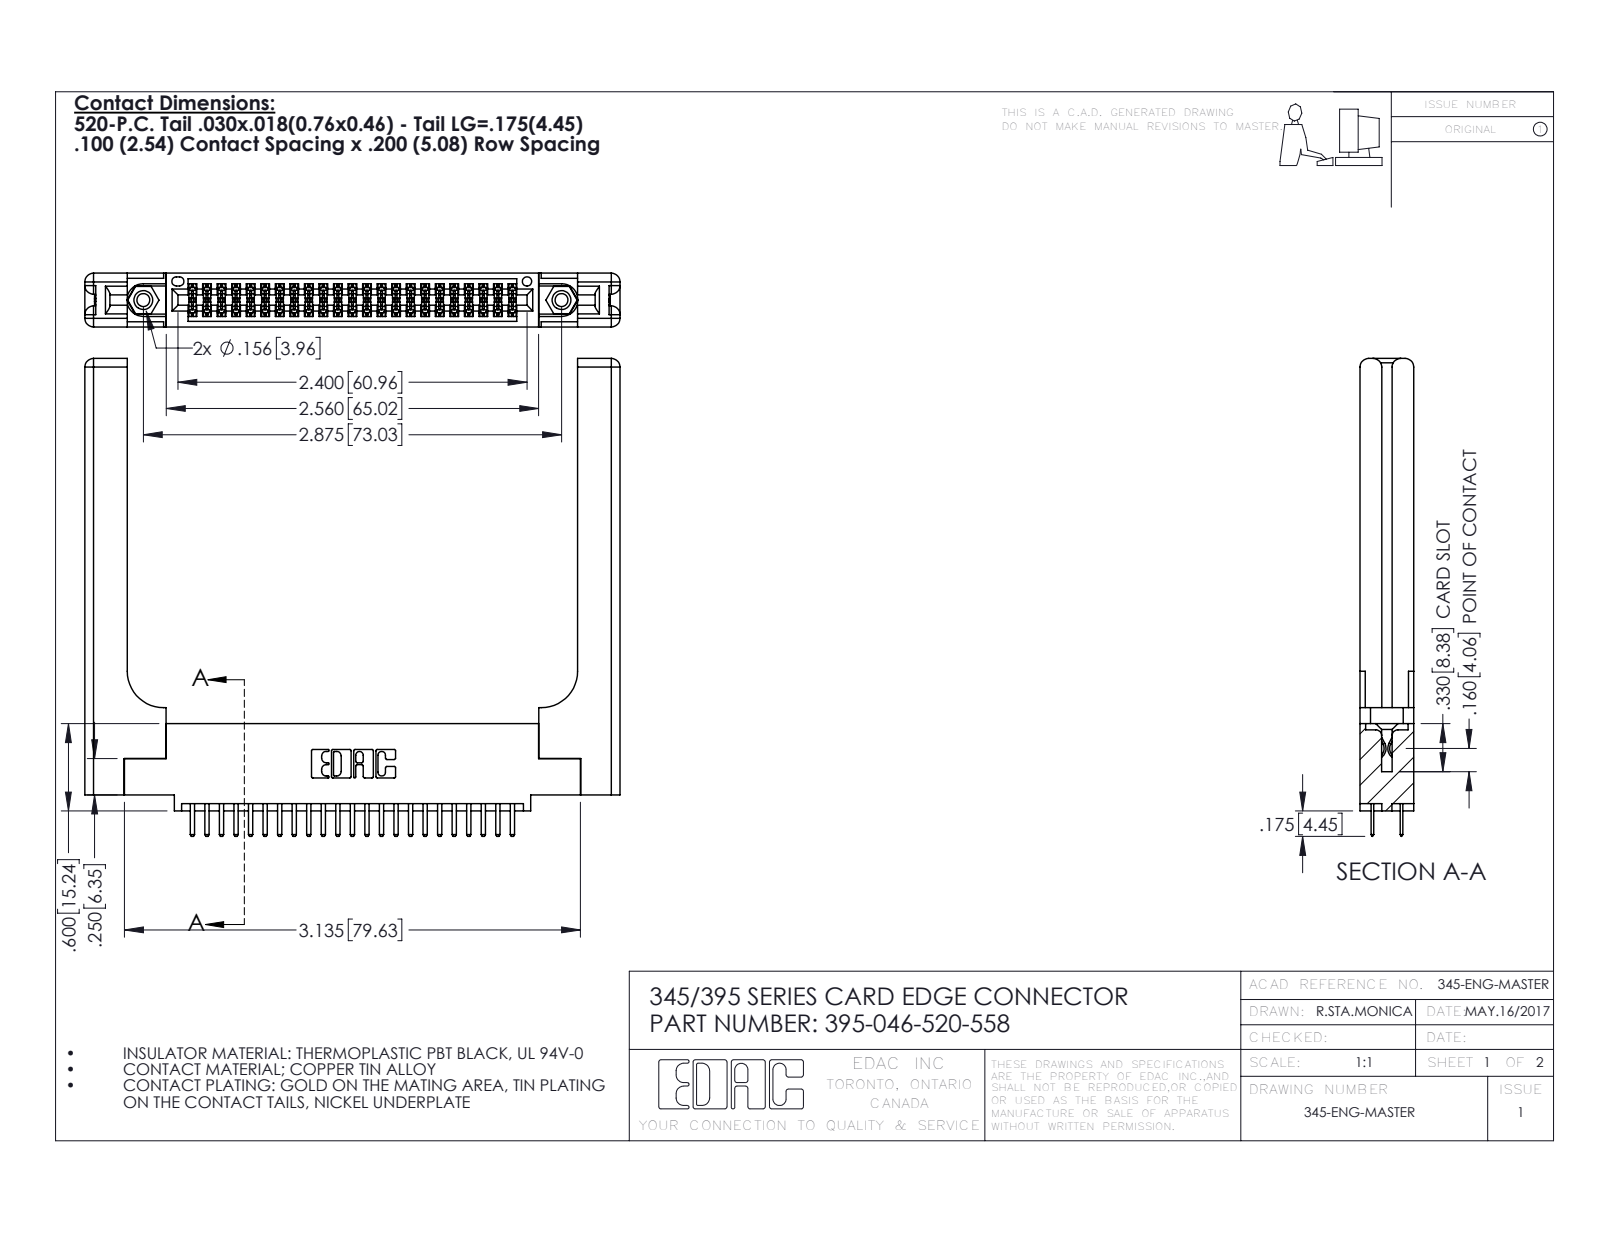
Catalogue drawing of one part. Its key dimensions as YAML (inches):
part_name: "345 Part_0.110 Offset - 0.156 Dia-TH; 345-250-001_345-250-001-102; 345-220-058_345-220-058; 345-292-001_345-293-120 (+1 more)"
step_written_by: "SolidWorks 2016 (CONFIG_CONTROL_DESIGN)"
units: inches
bodies: {solids: 51, faces: 2870, planar: 1842, cylindrical: 968, other: 60}
overall_size: [3.679, 3.285, 0.37]
volume: 1.055
surface_area: 27.53
round_holes:
  - {diameter: 0.089, count: 2}
  - {diameter: 0.125, count: 2}
  - {diameter: 0.156, count: 2}
  - {diameter: 0.064, count: 1}
round_bosses_or_shafts:
  - {diameter: 0.155, count: 2}
partial_cylinders:
  - {radius: 0.006, count: 69}
  - {radius: 0.01, count: 50}
  - {radius: 0.01, count: 22}
  - {radius: 0.06, count: 16}
  - {radius: 0.007, count: 6}
  - {radius: 0.031, count: 6}
  - {radius: 0.026, count: 3}
  - {radius: 0.014, count: 2}
face_to_face_distances: [0.37, 0.072, 0.298, 0.2, 0.15, 0.148, 0.22, 0.077, 0.098, 0.272]
hole_center_spacings: [0.27, 2.641, 2.875]
